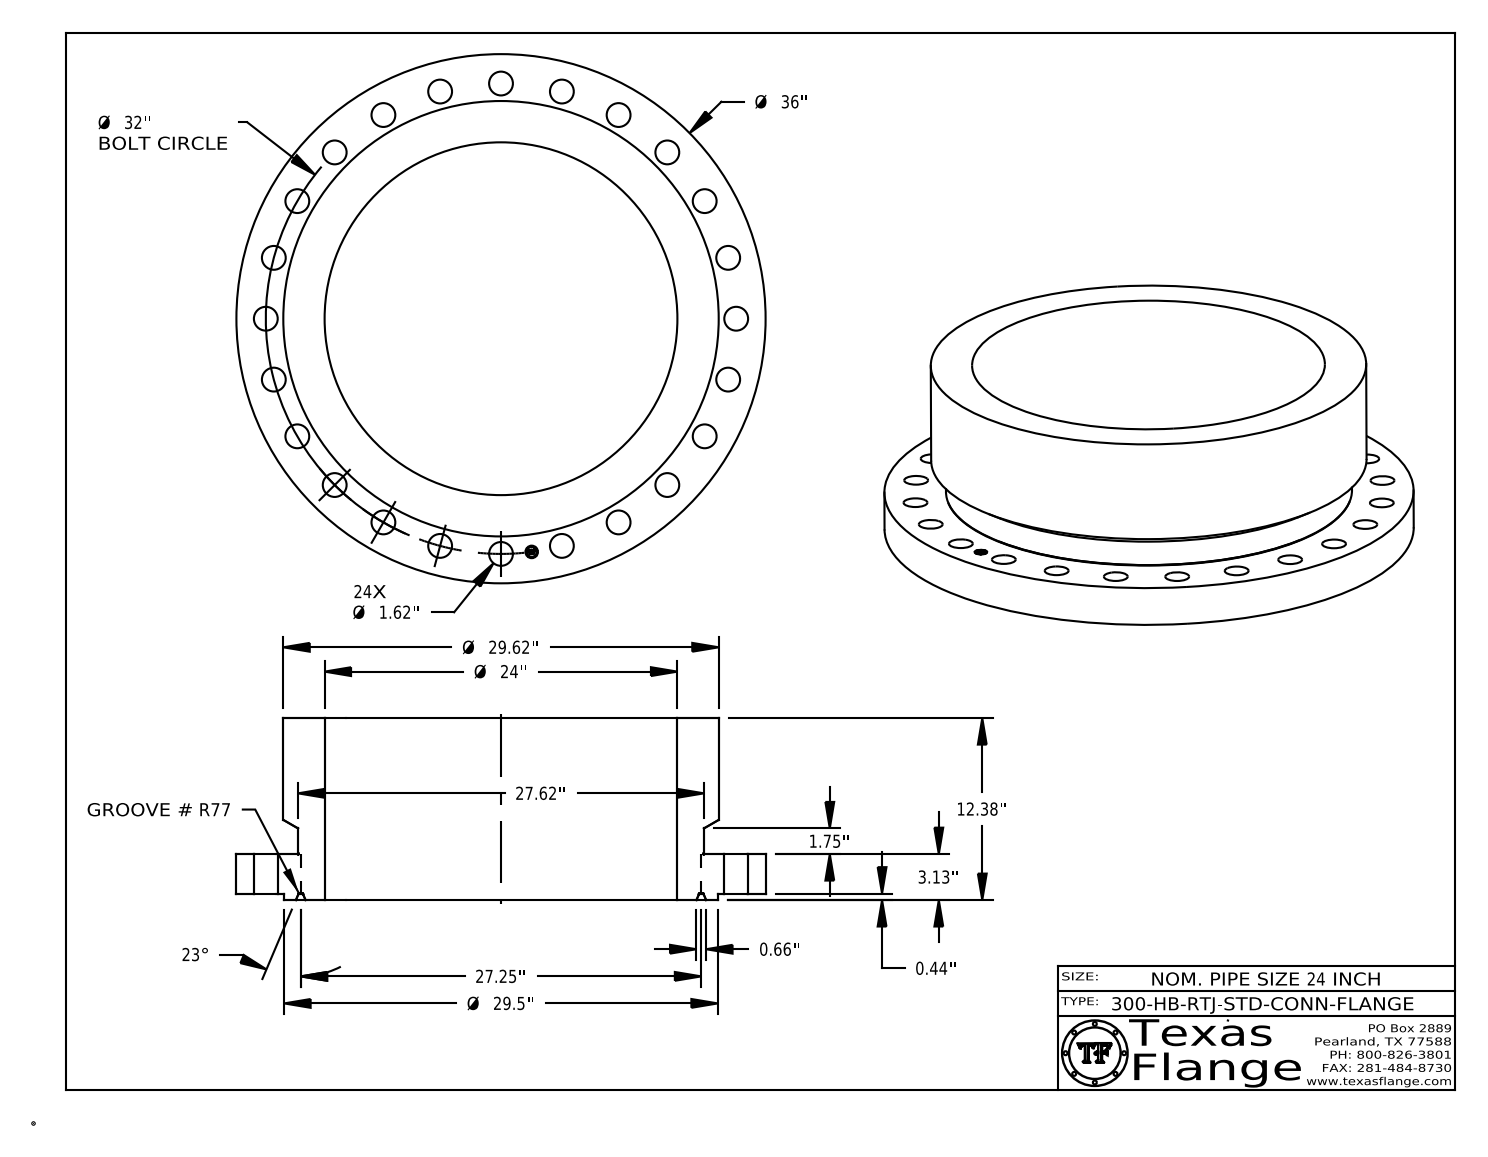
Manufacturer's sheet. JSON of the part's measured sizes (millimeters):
{"part_name": "24-300-HB-RTJ-STD-CONN-FLANGE", "step_written_by": "CATIA V5 STEP AP214 (AUTOMOTIVE_DESIGN)", "units": "millimeters", "bodies": {"solids": 1, "faces": 463, "planar": 371, "cylindrical": 78, "other": 14}, "overall_size": [914.4, 914.4, 314.4], "volume_mm3": 56960000, "surface_area_mm2": 2374000, "round_holes": [[41.1, 24], [21.6, 1], [609.6, 1]], "round_bosses_or_shafts": [[1.3, 8], [914.4, 1], [752.3, 1], [749.3, 1], [701.5, 1], [17, 1]], "face_to_face_distances": [68.2, 303.2, 235, 11.1, 79.4, 314.4, 79.3, 68.1, 235.1, 6.4], "hole_center_spacings": [406.4, 785.1, 106.1, 210.4, 311, 494.8, 574.7, 644.8]}
